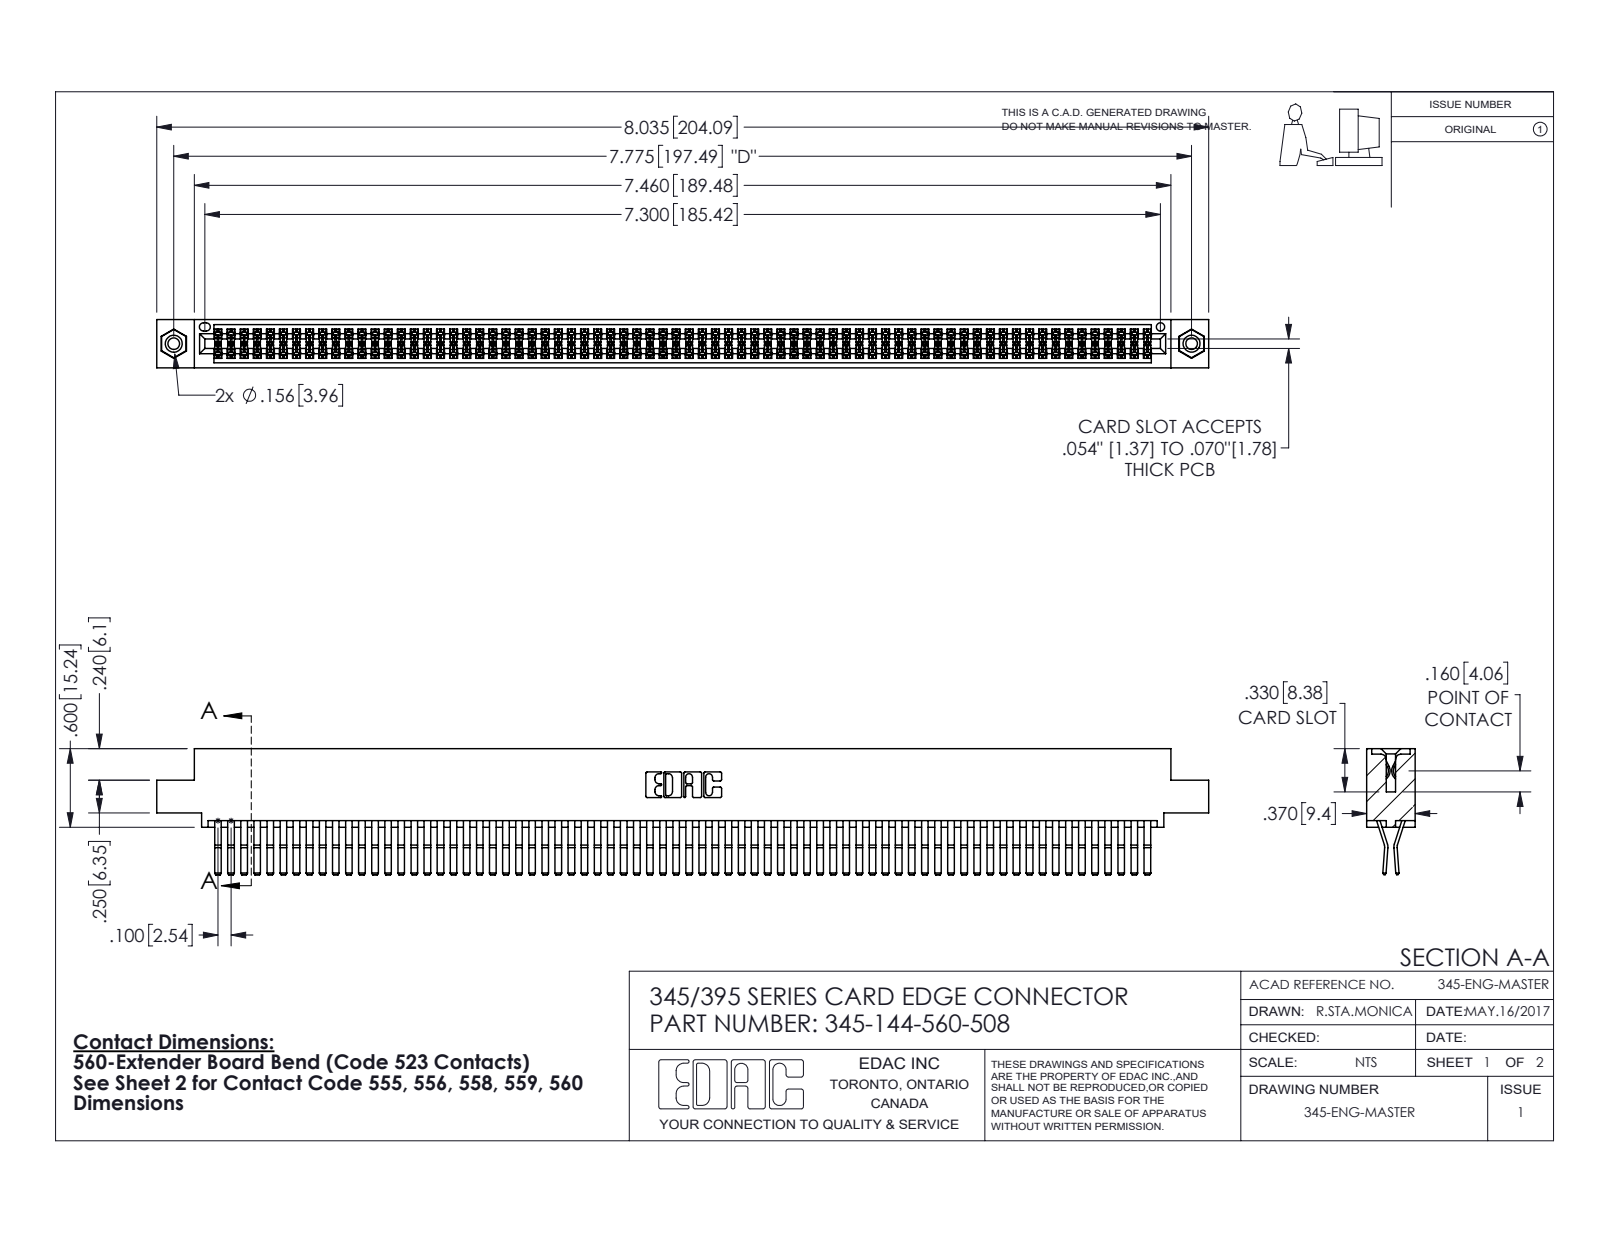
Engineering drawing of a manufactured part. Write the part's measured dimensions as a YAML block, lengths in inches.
part_name: "345-250-001_345-250-003-102; 345-144-560-508; 345-292-001_560 Tail; 345 Part_0.110 Offset - 0.156 Dia-TI"
step_written_by: "SolidWorks 2016 (CONFIG_CONTROL_DESIGN)"
units: inches
bodies: {solids: 147, faces: 7678, planar: 4868, cylindrical: 2794, other: 16}
overall_size: [8.035, 0.962, 0.37]
volume: 1.28
surface_area: 52.87
round_holes:
  - {diameter: 0.089, count: 2}
  - {diameter: 0.125, count: 2}
  - {diameter: 0.156, count: 2}
  - {diameter: 0.064, count: 1}
round_bosses_or_shafts:
  - {diameter: 0.155, count: 2}
partial_cylinders:
  - {radius: 0.006, count: 217}
  - {radius: 0.01, count: 22}
  - {radius: 0.007, count: 6}
  - {radius: 0.031, count: 6}
  - {radius: 0.026, count: 3}
  - {radius: 0.01, count: 2}
  - {radius: 0.014, count: 2}
  - {radius: 0.019, count: 2}
face_to_face_distances: [0.025, 0.072, 0.298, 0.37, 0.2, 0.098, 0.272, 0.225, 0.175, 0.149]
hole_center_spacings: [0.27, 7.539, 7.775]
